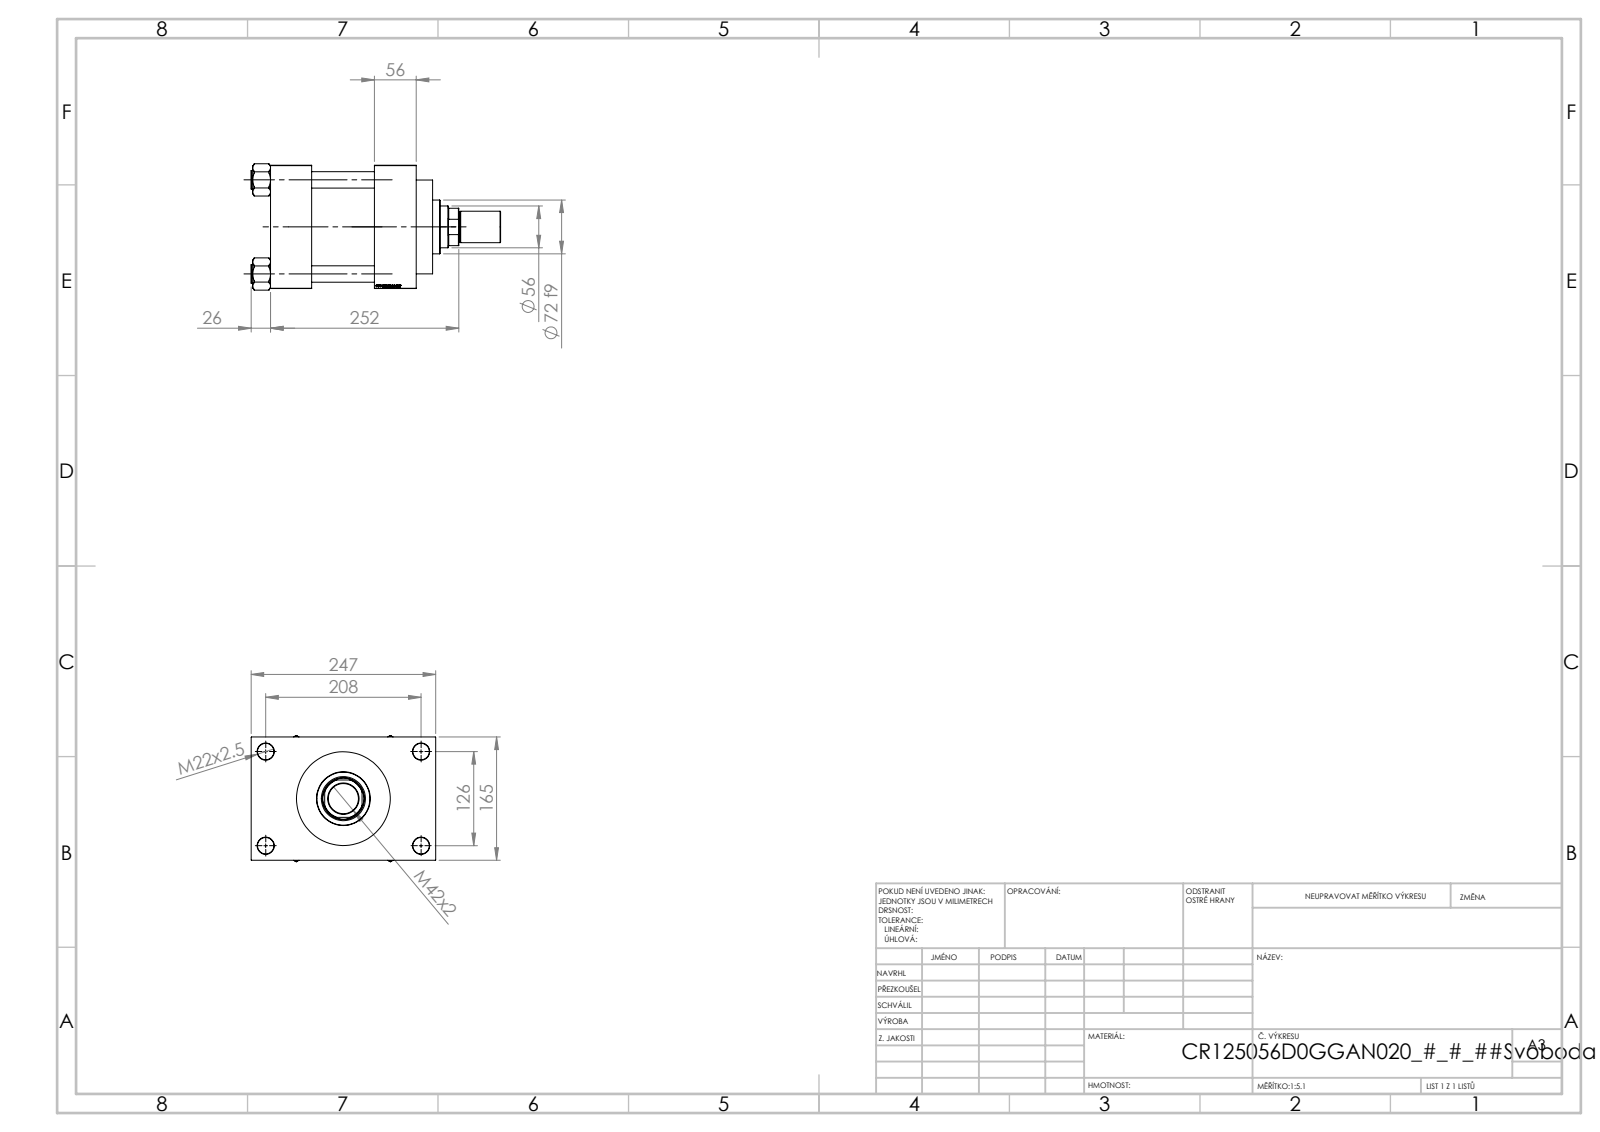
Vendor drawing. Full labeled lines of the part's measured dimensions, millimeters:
Part name (STEP PRODUCT): V215CR_VCP_D; NUT_M5_D; V215_VC_A; ROD_END_AH (+2 more)
STEP written by: SolidWorks 2019 (CONFIG_CONTROL_DESIGN)
Units: millimetres
Bodies: 12 solids, 1163 faces (548 planar, 91 cylindrical, 524 other)
Overall size (bounding box): 334 × 247 × 169.14
Volume: 5 035 000 mm³ · Surface area: 540 193 mm²
Round holes (diameter × count): ⌀22 ×8, ⌀7 ×2, ⌀32.24 ×2, ⌀45 ×2, ⌀40.5 ×1, ⌀56 ×1, ⌀59 ×1, ⌀96 ×1, ⌀125 ×1, ⌀125.5 ×1
Round bosses / shafts (diameter × count): ⌀25 ×4, ⌀131 ×1, ⌀72 ×1, ⌀42 ×1, ⌀40 ×1
Partial cylindrical surfaces — rounded edges, fillets, slot ends (radius × count): R27 ×1
Main face-to-face distances: 165, 84, 55, 139, 56, 195, 140, 41, 206, 173.74
Hole centre spacings: 41.05, 89.02, 121.59, 125.9, 132.47, 166.95, 209.13, 126
